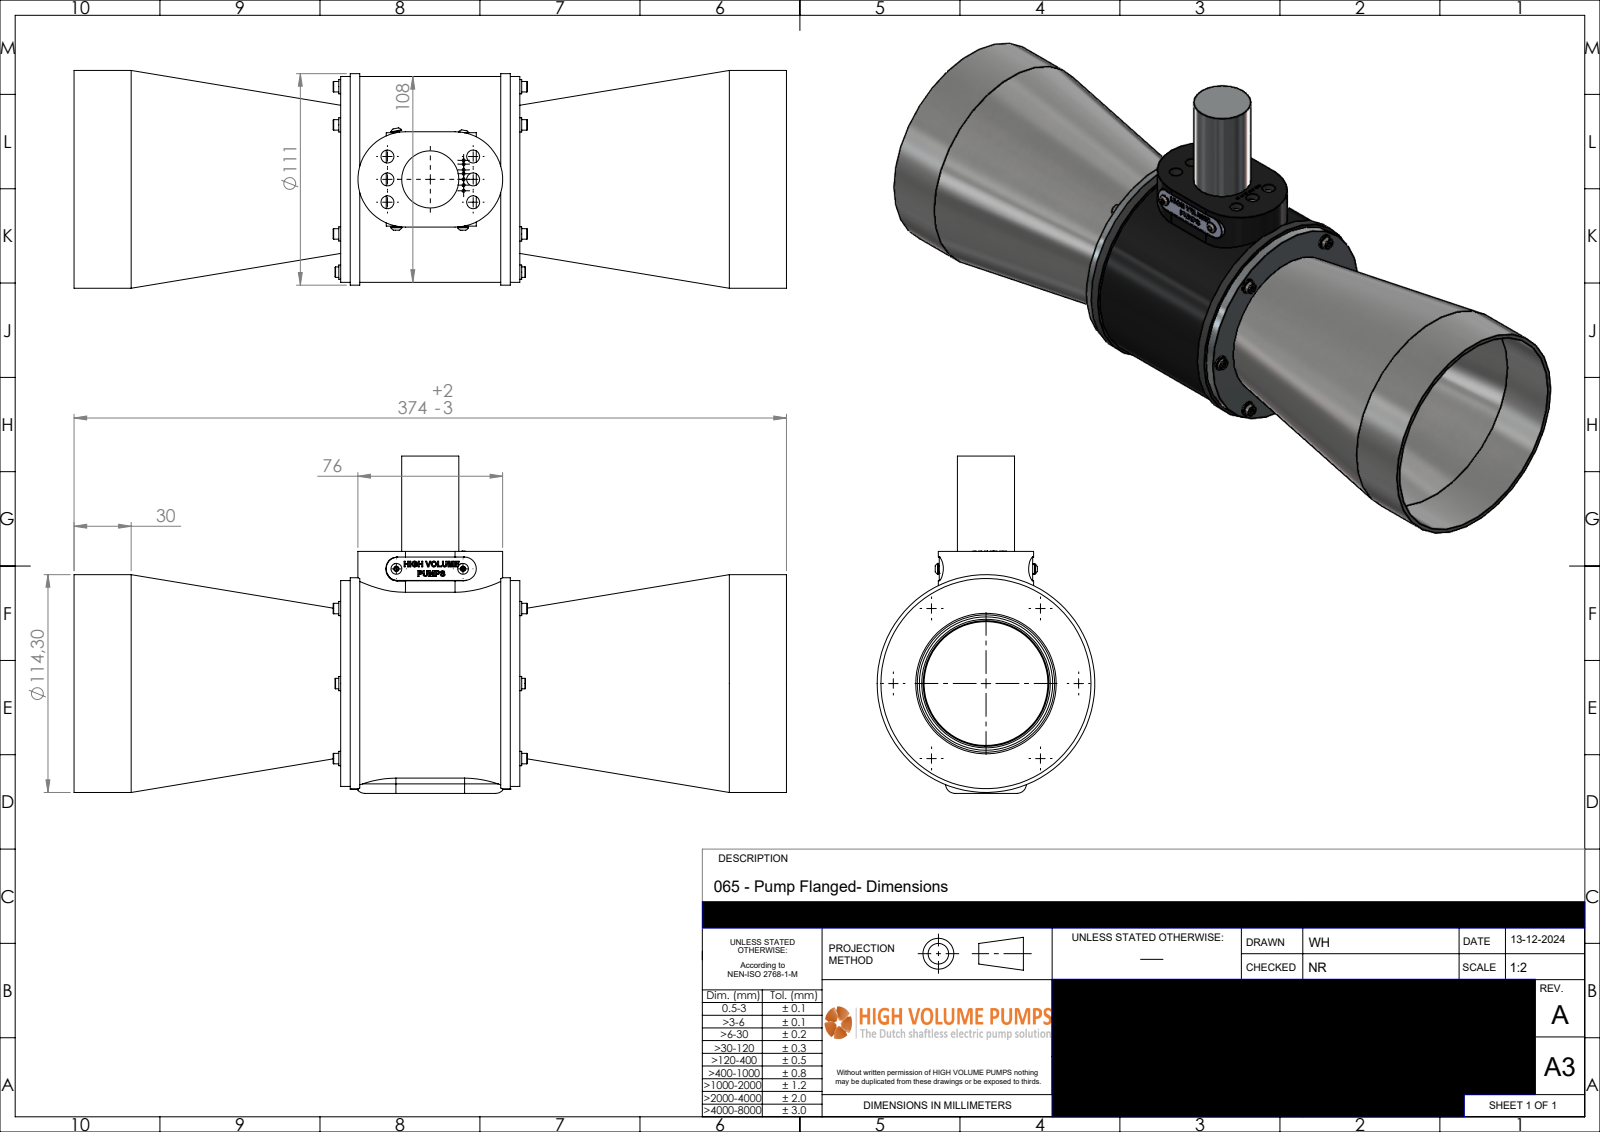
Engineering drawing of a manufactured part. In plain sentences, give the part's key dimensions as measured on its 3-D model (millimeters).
The part is named "P-065-030-rev-A-PUF". Its 3-D file was written by "SolidWorks 2024 (AUTOMOTIVE_DESIGN)". It is 1 solid with 1152 faces: 627 planar, 273 cylindrical and 252 other. Overall it measures 374 by 177.01 by 114.3 millimeters. Its volume is 799 446 cubic millimeters and its surface area 253 464 square millimeters. Round holes: 6 of diameter 3.2, 6 of diameter 6.8, 5 of diameter 3.6, 1 of diameter 65, 1 of diameter 67.5, 1 of diameter 70, 1 of diameter 72.1, 1 of diameter 110.3. Round bosses or shafts: 9 of diameter 3, 8 of diameter 5.7, 6 of diameter 7.5, 6 of diameter 5.5, 4 of diameter 1.55, 3 of diameter 1.6, 1 of diameter 114.3, 1 of diameter 111. Partial cylindrical surfaces (rounded edges, fillets, slot ends): 3 of radius 2, 2 of radius 1.75, 2 of radius 5, 2 of radius 6.15, 2 of radius 21.25, 2 of radius 24, 2 of radius 25, 1 of radius 1.5. The main face-to-face distances are 94, 5, 127.01, 84, 89, 140, 145, 229, 234, 10. The hole center spacings are 48.65, 12, 46.57, 45, 86.69, 24, 44.17, 51.
